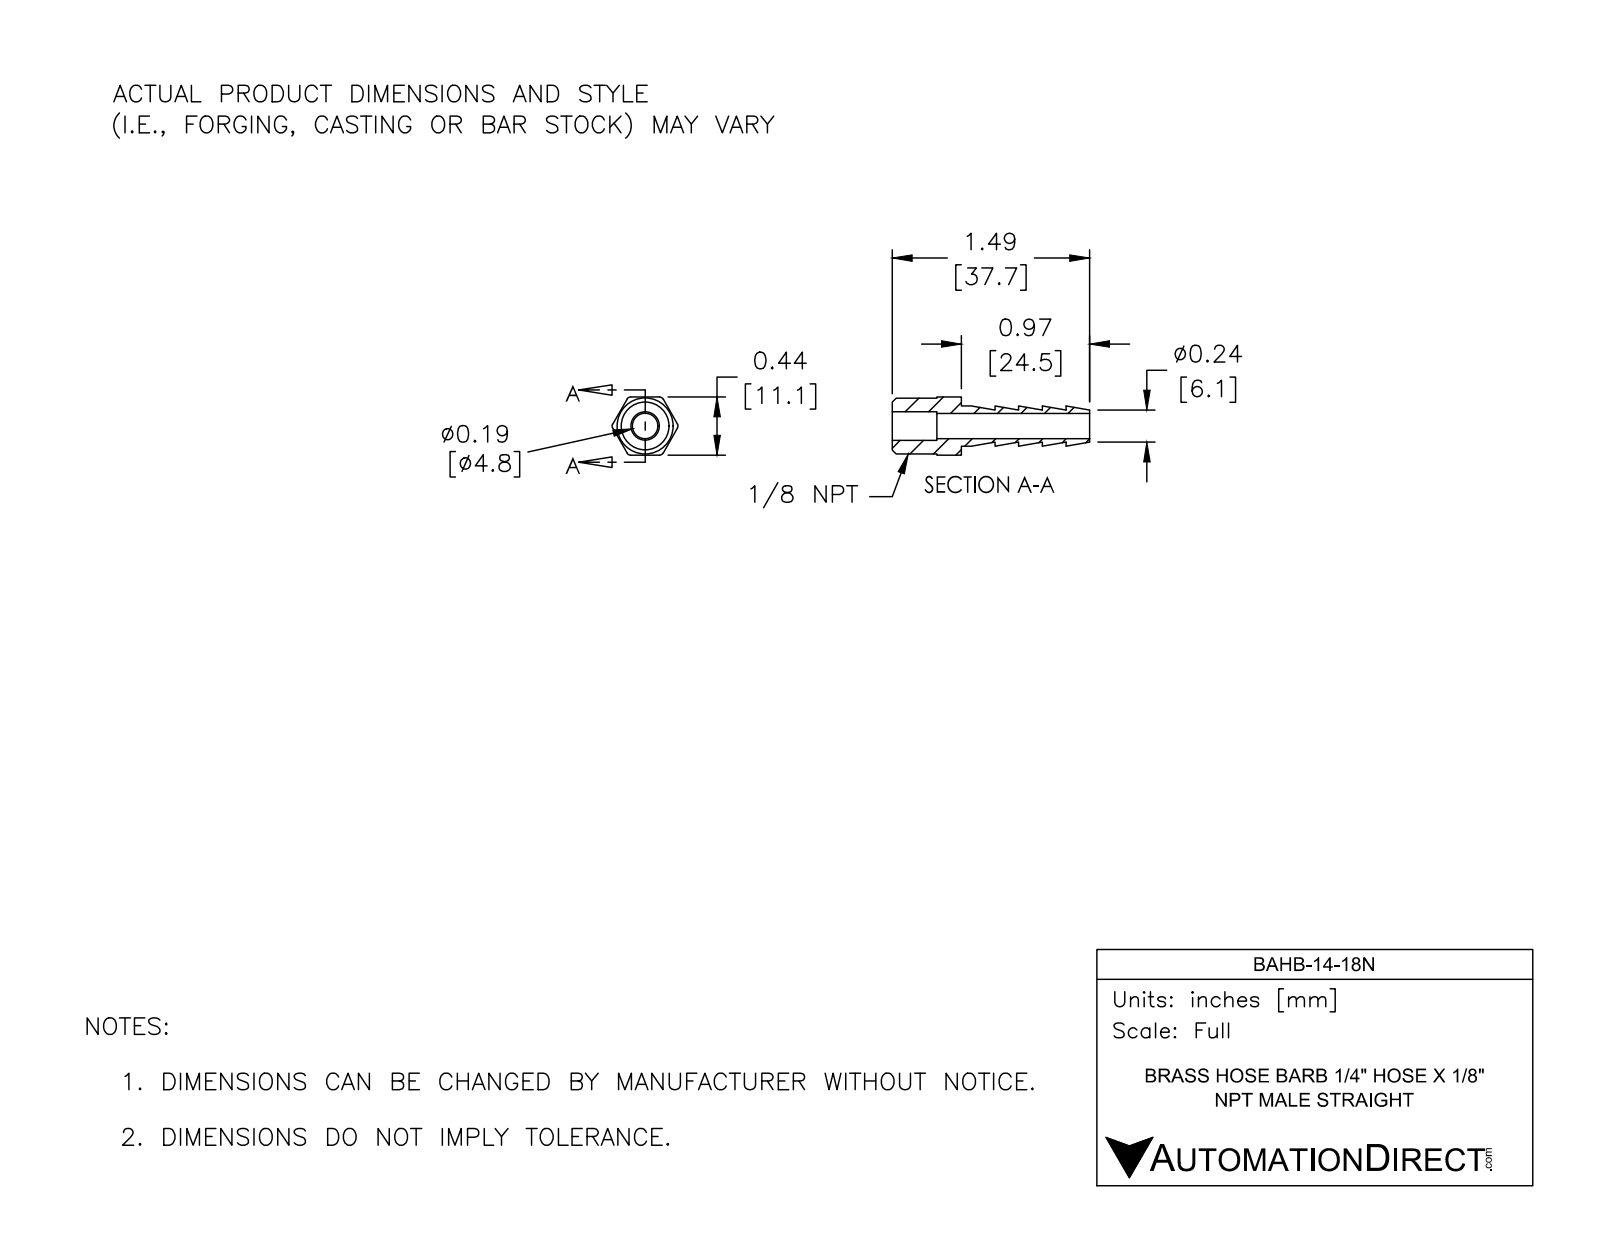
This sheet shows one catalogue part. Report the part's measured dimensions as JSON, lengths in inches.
{"part_name": "BAHB-14-18N", "step_written_by": "SolidWorks 2017 (AUTOMOTIVE_DESIGN)", "units": "inches", "bodies": {"solids": 1, "faces": 41, "planar": 15, "cylindrical": 12, "other": 14}, "overall_size": [1.486, 0.496, 0.438], "volume_in3": 0.087, "surface_area_in2": 2.785, "round_holes": [[0.19, 1], [0.215, 1]], "round_bosses_or_shafts": [[0.303, 1]], "partial_cylinders_radius": [[0.03, 6]], "face_to_face_distances": [0.438, 0.178, 0.521, 0.356, 0.534, 0.184, 0.337, 0.787, 0.971, 1.308]}
